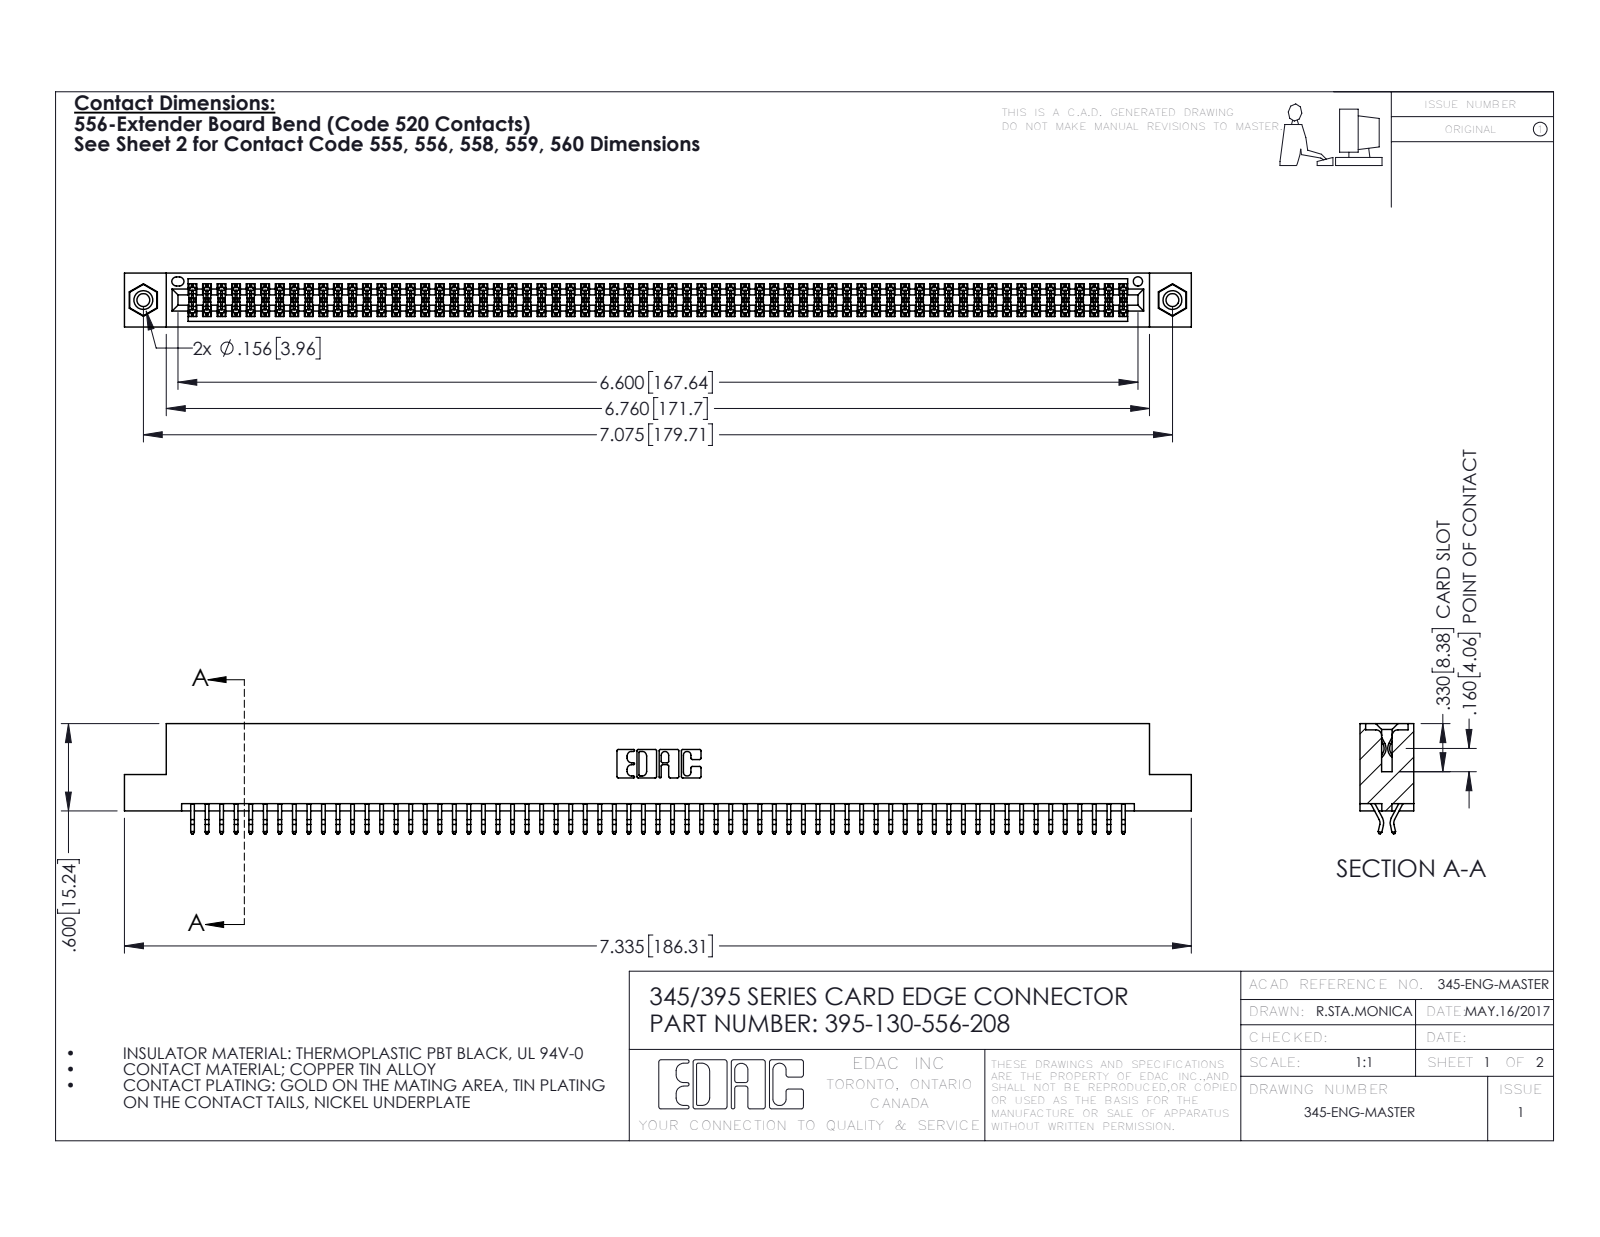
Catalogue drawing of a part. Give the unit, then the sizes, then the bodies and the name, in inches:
Units: inches
Overall size (bounding box): 7.335 × 0.757 × 0.37
Round holes (diameter × count): ⌀0.089 ×2, ⌀0.125 ×2, ⌀0.156 ×2, ⌀0.064 ×1
Round bosses / shafts (diameter × count): ⌀0.155 ×2
Partial cylindrical surfaces — rounded edges, fillets, slot ends (radius × count): R0.006 ×195, R0.01 ×22, R0.007 ×6, R0.031 ×6, R0.026 ×3, R0.01 ×2, R0.014 ×2, R0.019 ×2
Main face-to-face distances: 0.072, 0.298, 0.37, 0.2, 0.025, 0.098, 0.272, 0.225, 0.175, 0.149
Hole centre spacings: 0.27, 6.839, 7.075
Volume: 1.117 in³ · Surface area: 42.46 in²
Bodies: 133 solids, 7466 faces (4922 planar, 2528 cylindrical, 16 other)
Part name (STEP PRODUCT): 345-292-001_556 Tail; 395-130-556-208; 345-250-001_345-250-003-102; 345 Part_Flush Mounting Lugs - 0.156 Dia-TI
STEP written by: SolidWorks 2016 (CONFIG_CONTROL_DESIGN)
